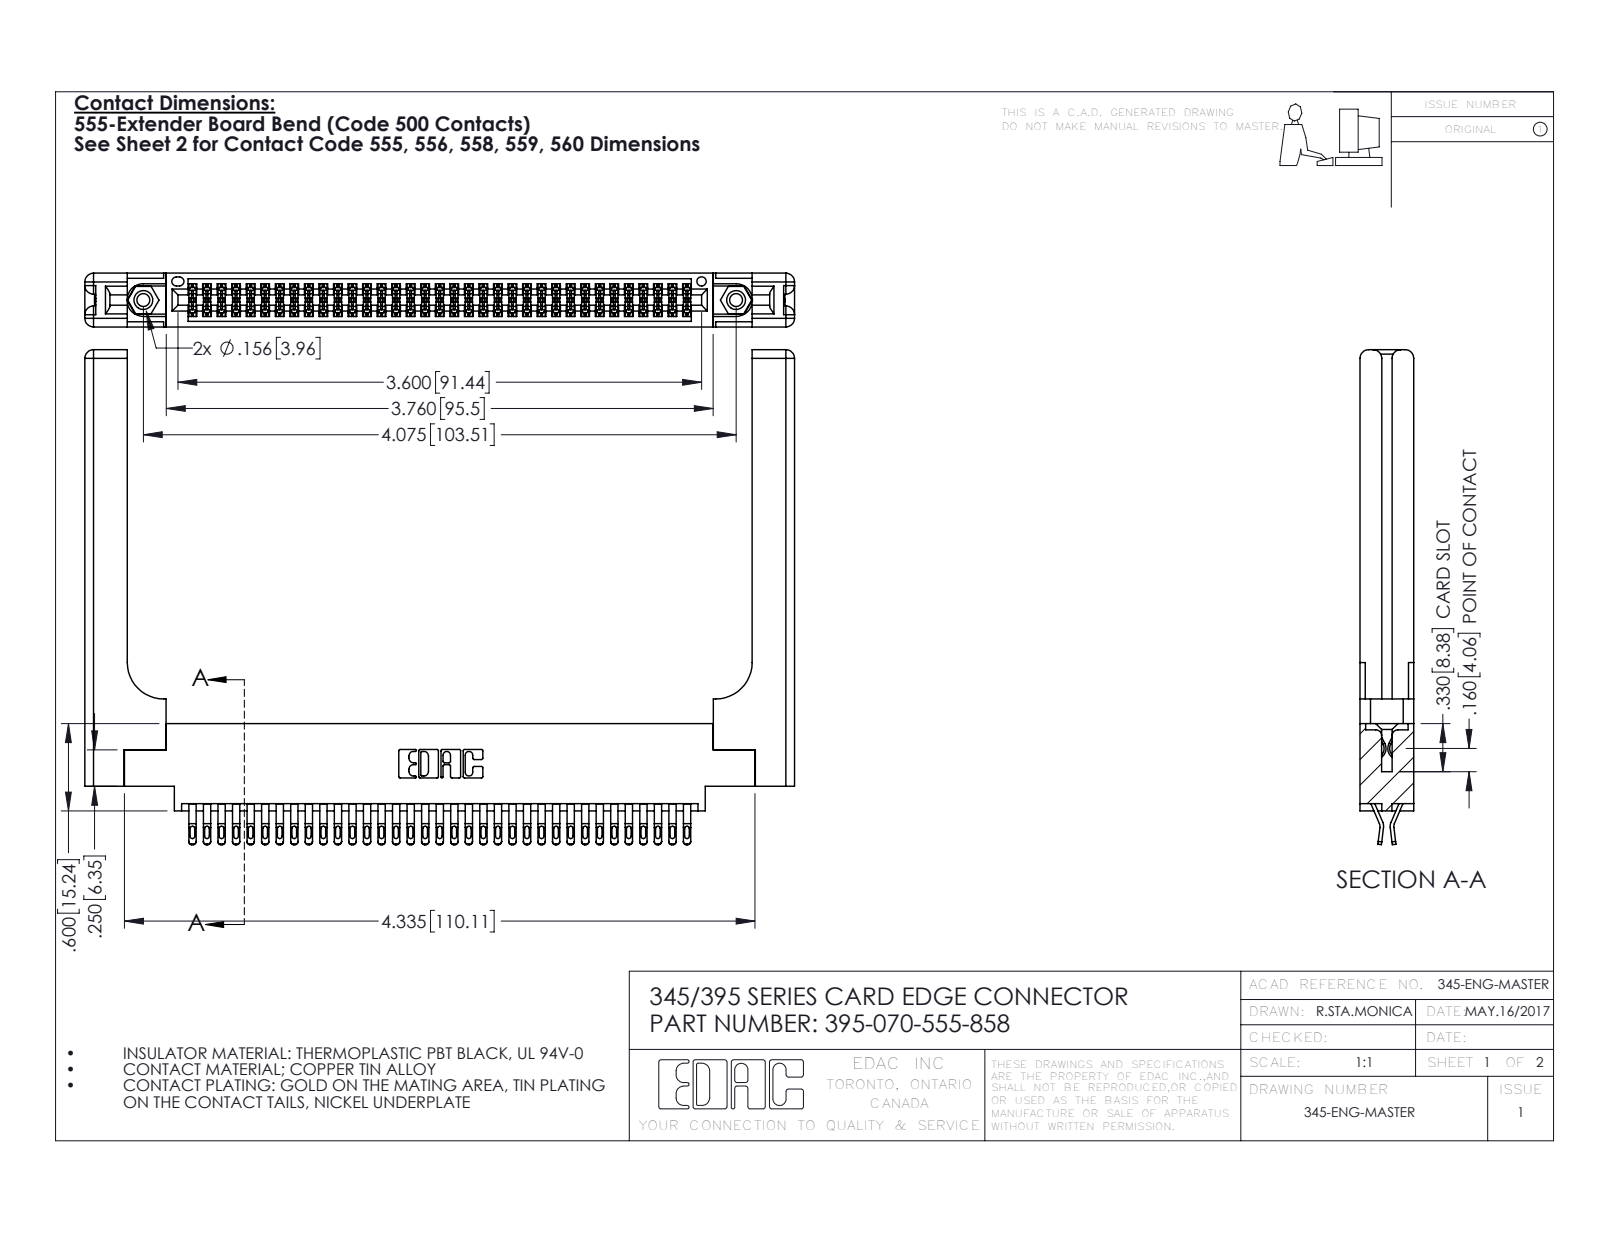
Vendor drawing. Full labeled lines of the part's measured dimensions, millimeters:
Part name (STEP PRODUCT): 345-220-058_345-220-058; 345-292-001_555 Tail; 345 Part_0.170 Offset - 0.156 Dia-TH; 395-070-555-858 (+1 more)
STEP written by: SolidWorks 2016 (CONFIG_CONTROL_DESIGN)
Units: millimetres
Bodies: 75 solids, 4306 faces (2402 planar, 1844 cylindrical, 60 other)
Overall size (bounding box): 123.9 × 86.4 × 9.4
Volume: 20 530 mm³ · Surface area: 23 610 mm²
Round holes (diameter × count): ⌀2.3 ×2, ⌀3.2 ×2, ⌀4 ×2, ⌀1.6 ×1
Round bosses / shafts (diameter × count): ⌀3.9 ×2
Partial cylindrical surfaces — rounded edges, fillets, slot ends (radius × count): R0.4 ×175, R0.5 ×140, R0.2 ×105, R0.3 ×22, R1.5 ×16, R0.2 ×6, R0.8 ×6, R0.7 ×3
Main face-to-face distances: 9.4, 1.8, 7.6, 0.6, 2.5, 6.9, 5.1, 5.7, 3.8, 3.8
Hole centre spacings: 6.9, 97.5, 103.5
